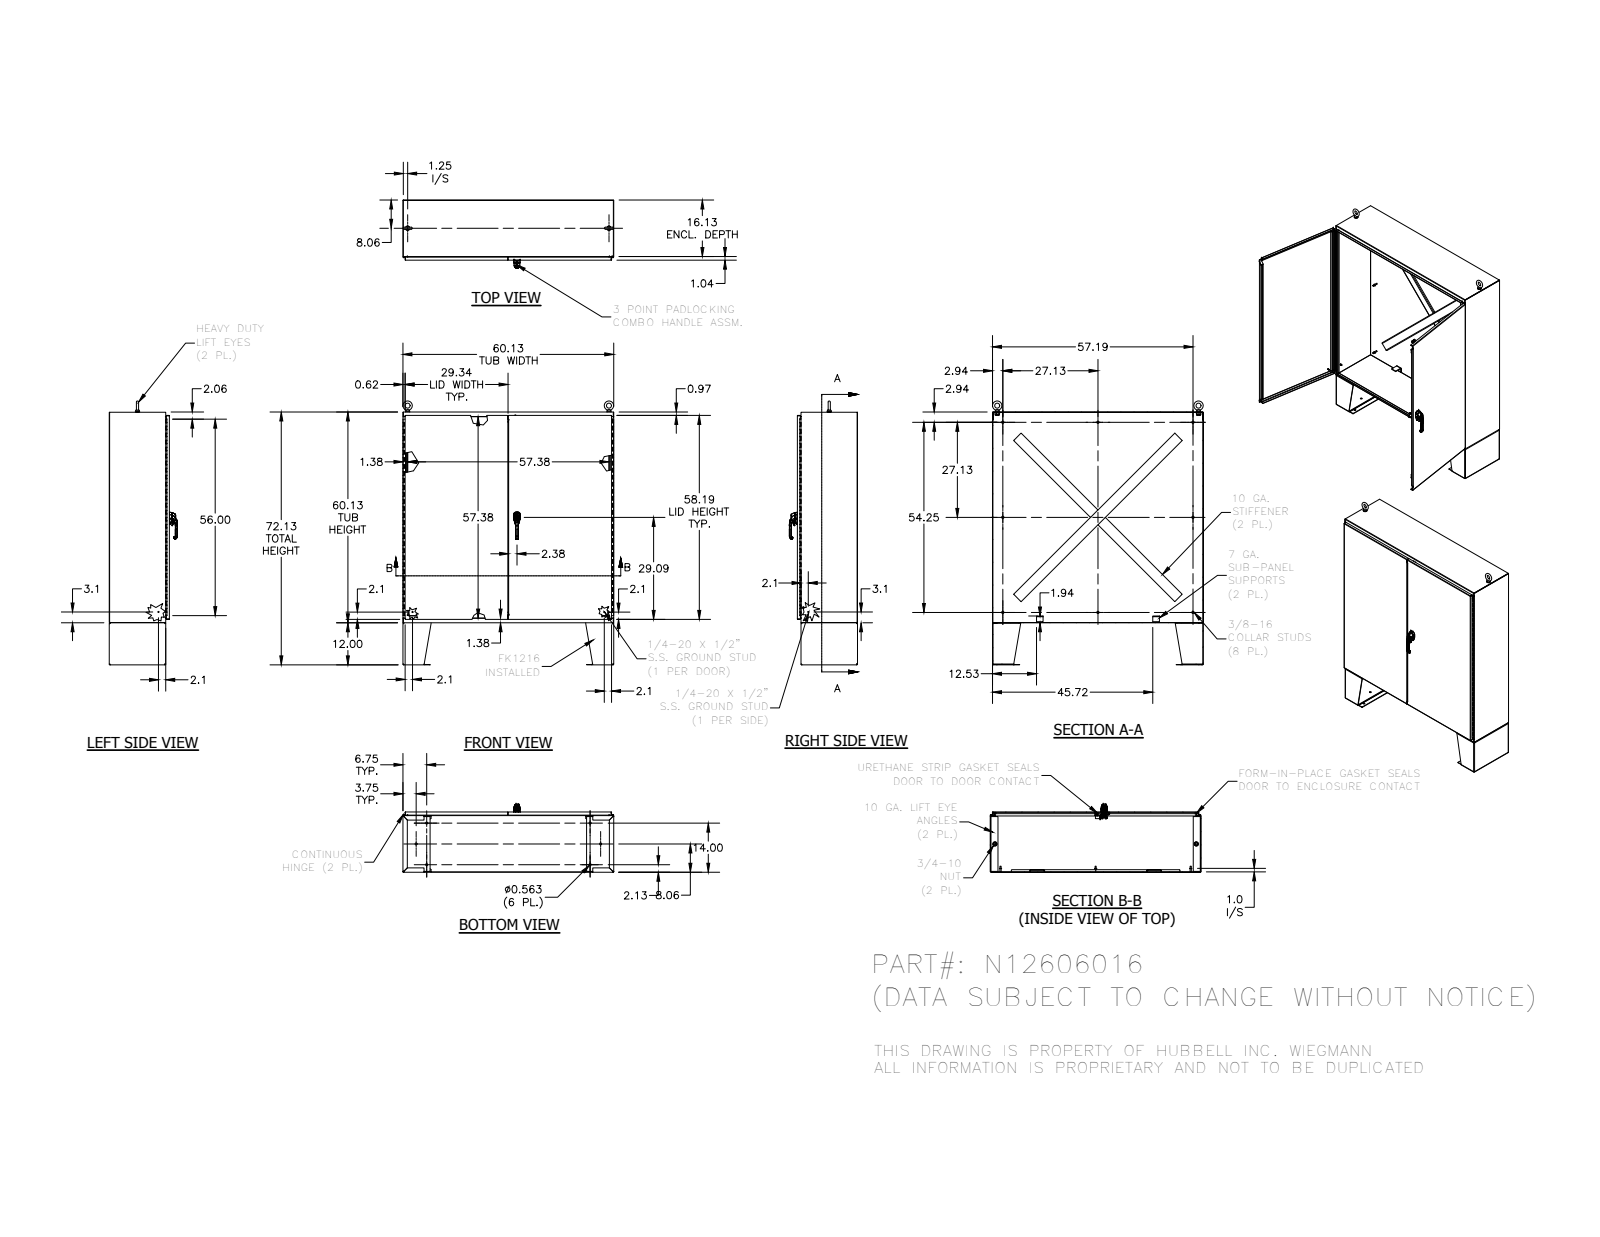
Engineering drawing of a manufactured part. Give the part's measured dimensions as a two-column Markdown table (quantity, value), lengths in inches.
| quantity | value |
| --- | --- |
| part name | N12606016 |
| STEP written by | SolidWorks 2018 (AUTOMOTIVE_DESIGN) |
| units | inches |
| bodies | 76 solids, 2392 faces (1384 planar, 708 cylindrical, 300 other) |
| overall size | 75.248 × 60.551 × 19.338 |
| volume | 1 421 in³ |
| surface area | 28 510 in² |
| round holes (diameter × count) | 0.563 × 18, 0.277 × 8, 0.2 × 4, 0.28 × 3, 0.125 × 2, 0.125 × 2, 0.241 × 2, 0.25 × 2, 0.252 × 2, 0.4 × 2, 0.45 × 2, 0.642 × 2 |
| round bosses / shafts (diameter × count) | 0.33 × 8, 0.625 × 6, 0.25 × 5, 0.337 × 3, 1.25 × 2, 1.12 × 2, 1 × 2, 0.75 × 2 |
| partial cylindrical surfaces (radius × count) | 0.031 × 24, 0.094 × 23, 0.219 × 22, 0.05 × 18, 0.025 × 16, 0.125 × 15, 0.03 × 13, 0.067 × 8 |
| main face-to-face distances | 0.094, 17.067, 60.031, 16.973, 17.16, 60.125, 59.938, 0.125, 16.031, 1.035 |
| hole center spacings | 5, 5.85, 6.57, 6.652, 8.03, 14.75, 15.574, 46.398 |
